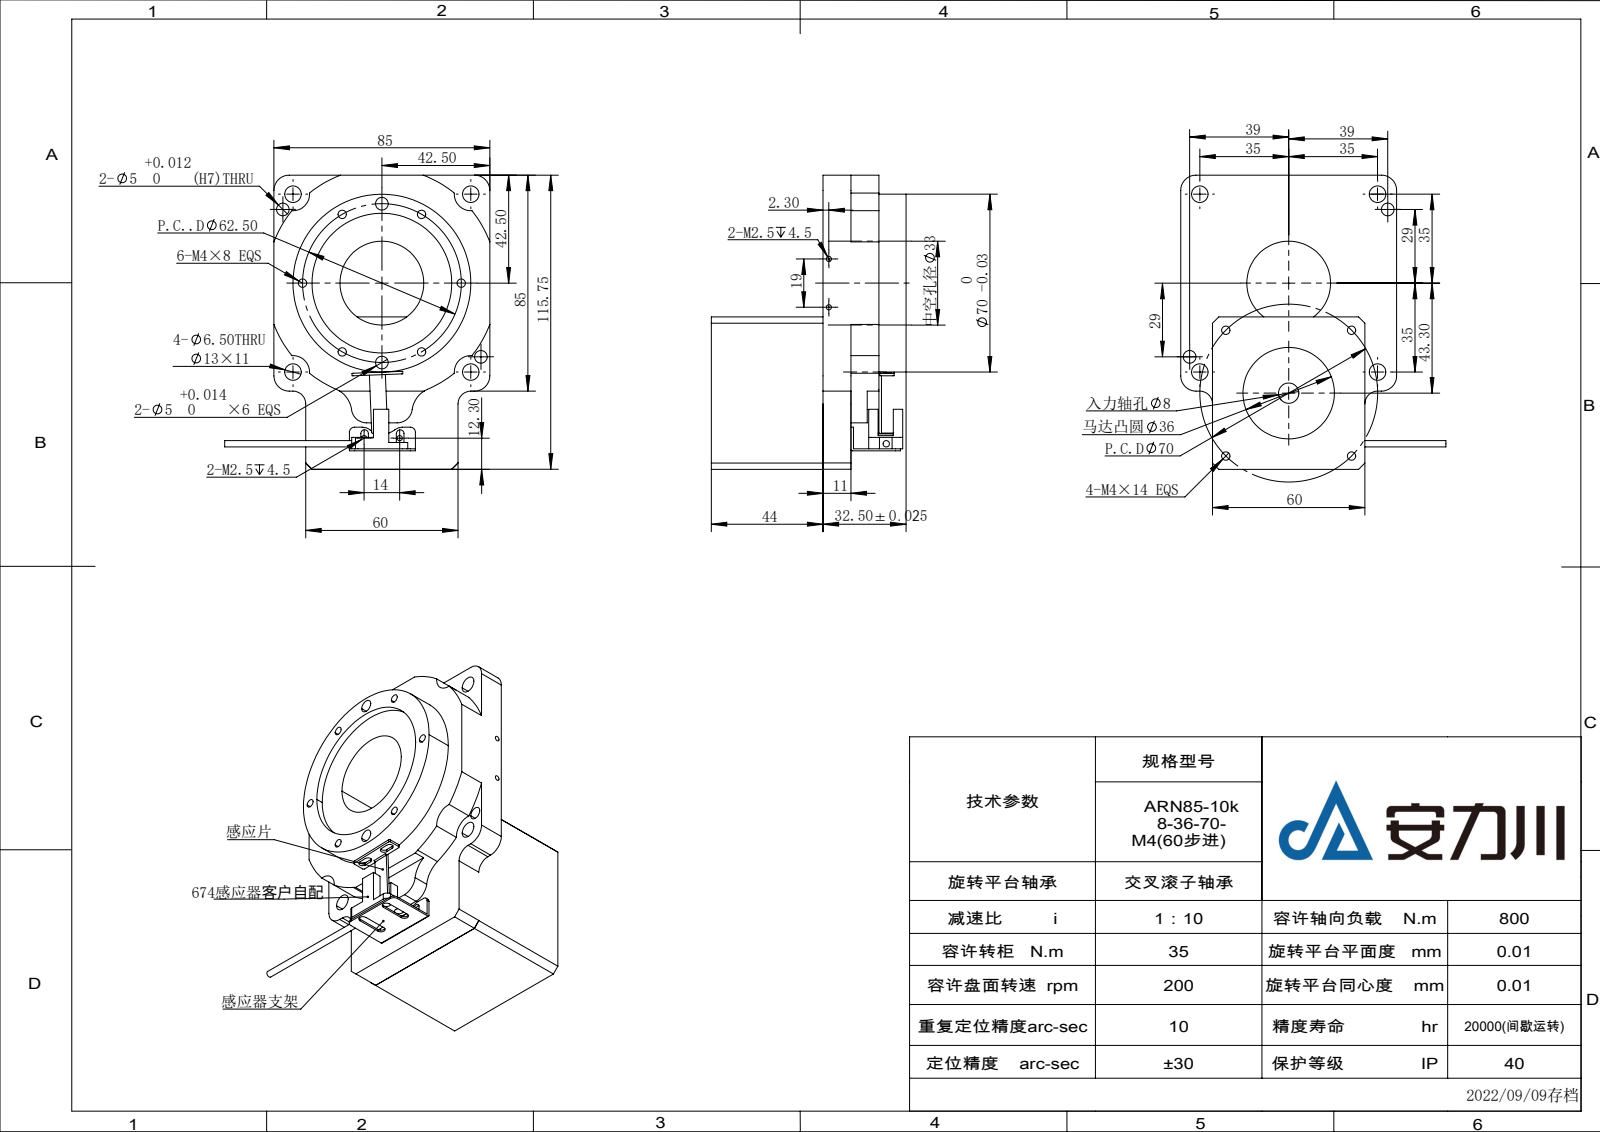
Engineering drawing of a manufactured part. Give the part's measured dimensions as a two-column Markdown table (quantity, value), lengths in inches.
| quantity | value |
| --- | --- |
| part name | KTN85-10K-8-36--70-M4(60步进); 感应器支架; SX674; 感应片1 |
| STEP written by | SolidWorks 2020 (AUTOMOTIVE_DESIGN) |
| units | inches |
| bodies | 4 solids, 283 faces (117 planar, 126 cylindrical, 40 other) |
| overall size | 4.559 × 4.11 × 3.012 |
| volume | 19.89 in³ |
| surface area | 74.42 in² |
| round holes (diameter × count) | 0.13 × 10, 0.081 × 6, 0.197 × 4, 0.256 × 4, 0.138 × 2, 0.315 × 1, 1.299 × 1, 1.417 × 1, 2.165 × 1 |
| round bosses / shafts (diameter × count) | 2.756 × 1, 0.098 × 1 |
| partial cylindrical surfaces (radius × count) | 0.02 × 9, 0.059 × 8, 0.079 × 6, 0.236 × 6, 0.065 × 4, 0.197 × 4, 0.256 × 4, 0.039 × 2 |
| main face-to-face distances | 0.433, 2.362, 2.165, 1.732, 2.598, 0.866, 0.492, 2.854, 1.169, 2.902 |
| hole center spacings | 1.23, 1.386, 1.949, 2.95, 2.756, 1.23, 1.378, 1.74 |
